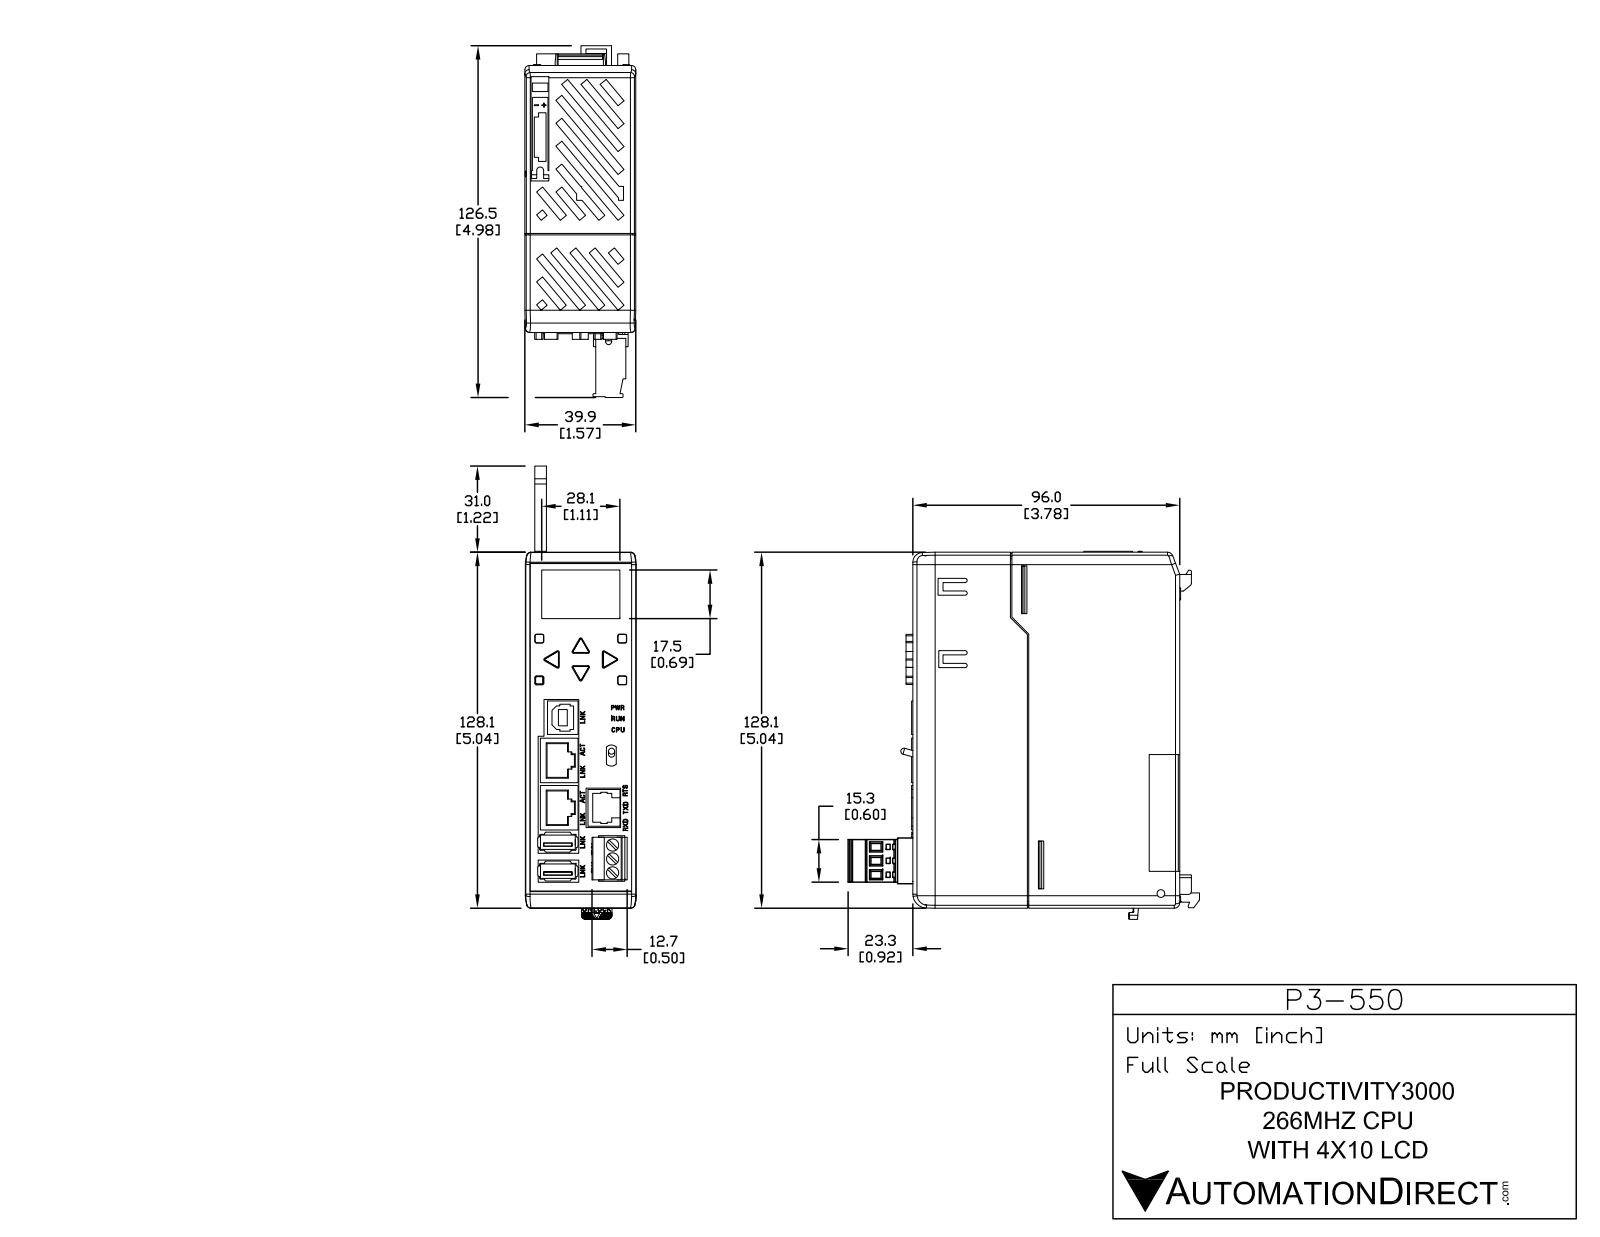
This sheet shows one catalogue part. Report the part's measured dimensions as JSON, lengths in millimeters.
{"part_name": "P3-550", "step_written_by": "SolidWorks 2009 (CONFIG_CONTROL_DESIGN)", "units": "millimeters", "bodies": {"solids": 1, "faces": 2336, "planar": 2053, "cylindrical": 218, "other": 65}, "overall_size": [132.38, 121.28, 39.9], "volume_mm3": 489688, "surface_area_mm2": 47441, "round_holes": [[1.4, 3], [4.4, 3], [2.2, 1], [2.8, 1]], "round_bosses_or_shafts": [[3, 3], [2.2, 1]], "partial_cylinders_radius": [[0.5, 29], [0.3, 21], [0.62, 16], [1.5, 14], [0.6, 12], [1, 10], [0.1, 8], [3.5, 7]], "face_to_face_distances": [39.9, 0.5, 95.83, 127.58, 128.08, 127.08, 95.33, 95.53, 95.03, 39.4], "hole_center_spacings": [5, 0.5, 4.97, 5.08, 10, 9.95, 10.07, 125.01]}
